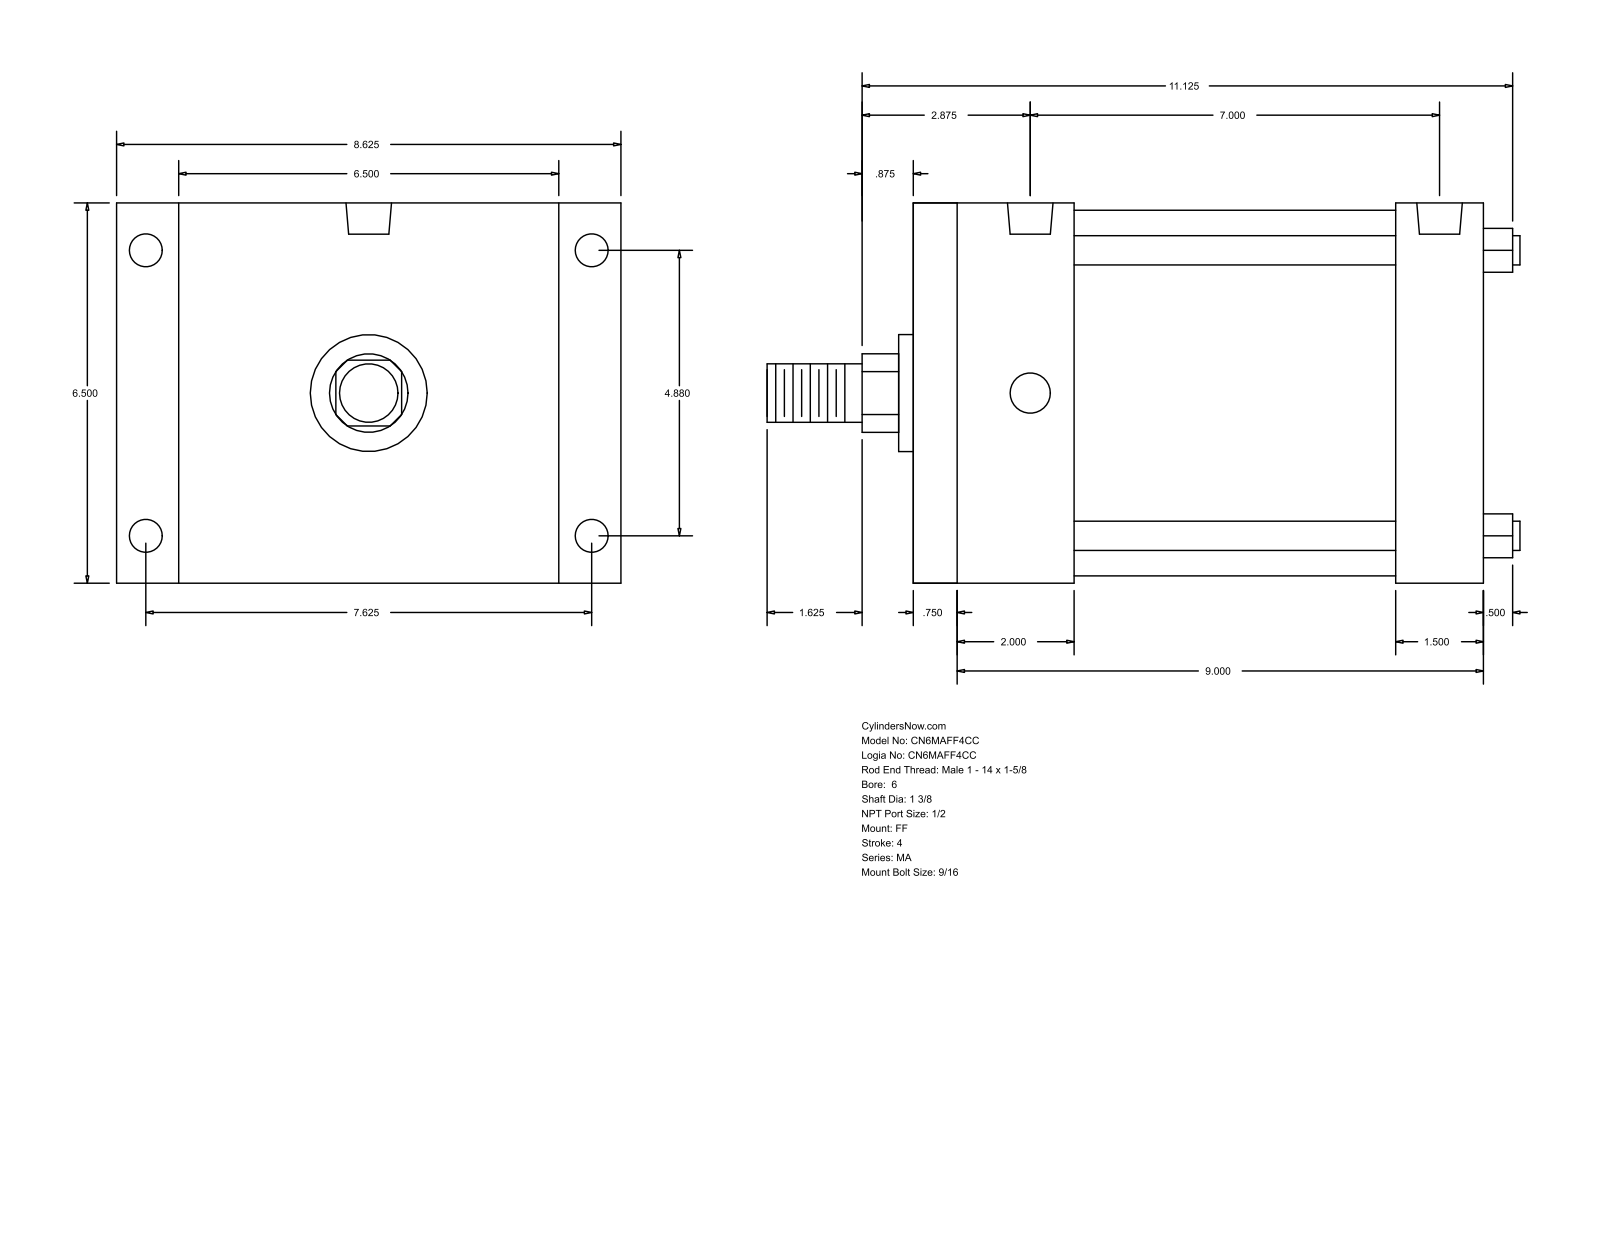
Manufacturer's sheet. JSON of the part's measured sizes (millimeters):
{"part_name": "MA_FF__0600_1.375", "step_written_by": "GSSL Pune (CONFIG_CONTROL_DESIGN)", "units": "millimeters", "bodies": {"solids": 0, "faces": 92, "planar": 64, "cylindrical": 28, "other": 0}, "overall_size": [327.02, 219.07, 165.1], "round_holes": [[14.29, 4], [17.46, 4], [19.77, 2]], "round_bosses_or_shafts": [[12.7, 4], [158.75, 1], [50.8, 1], [34.92, 1], [25.4, 1]], "partial_cylinders_radius": [[17.06, 1]], "face_to_face_distances": [165.1, 247.65, 15.87, 231.78, 38.1, 66.67, 50.8, 180.98, 209.55, 193.68], "hole_center_spacings": [123.96, 180.97, 193.68, 229.95, 3.18, 177.79]}
